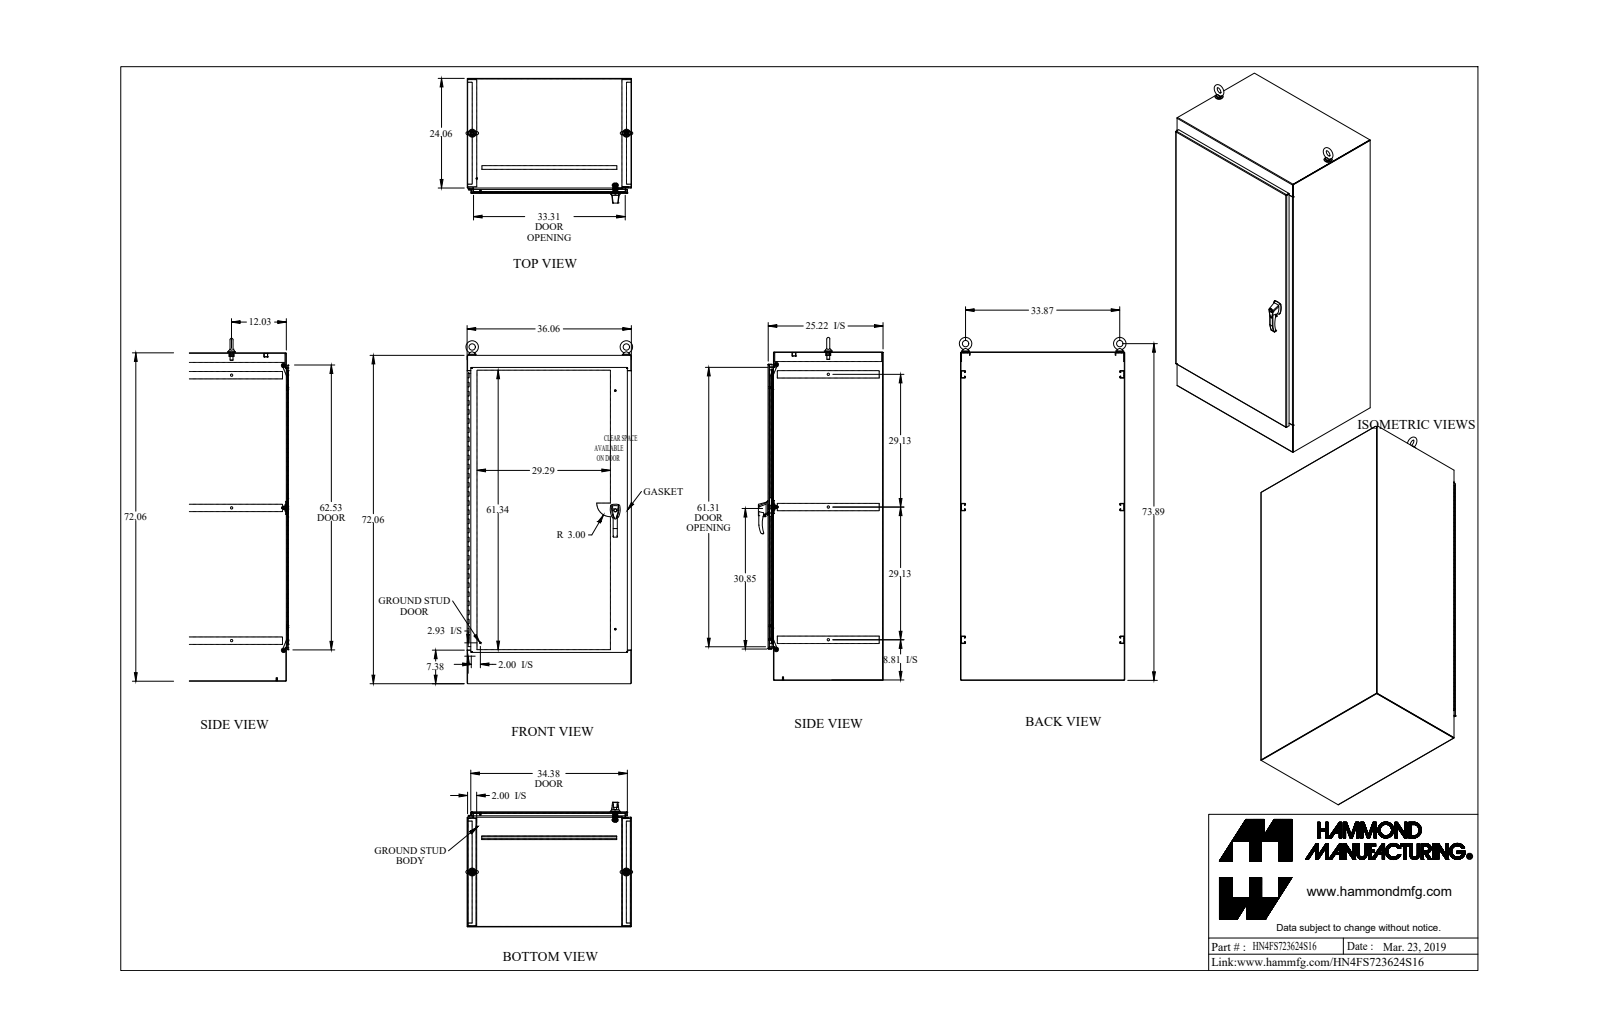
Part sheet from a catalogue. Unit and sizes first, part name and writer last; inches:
Units: inches
Overall size (bounding box): 75.489 × 36.604 × 27.362
Round holes (diameter × count): ⌀0.304 ×10, ⌀0.35 ×7, ⌀0.5 ×3, ⌀0.25 ×2, ⌀0.257 ×2, ⌀0.28 ×2, ⌀0.281 ×2, ⌀0.313 ×2, ⌀0.39 ×2, ⌀0.413 ×2, ⌀0.527 ×2, ⌀0.68 ×2
Round bosses / shafts (diameter × count): ⌀1.75 ×2, ⌀1.5 ×2, ⌀1.25 ×2, ⌀1 ×2, ⌀0.75 ×2, ⌀0.738 ×2, ⌀0.63 ×2, ⌀0.625 ×2
Partial cylindrical surfaces — rounded edges, fillets, slot ends (radius × count): R0.043 ×42, R0.138 ×36, R0.5 ×23, R0.125 ×22, R0.018 ×16, R0.06 ×15, R0.048 ×13, R0.143 ×13
Main face-to-face distances: 0.095, 25.152, 35.965, 25.057, 25.247, 35.87, 36.06, 71.965, 23.965, 1.187
Hole centre spacings: 6, 12, 18, 24, 30, 36, 42, 0.015
Volume: 1 180 in³ · Surface area: 24 827 in²
Bodies: 57 solids, 1892 faces (877 planar, 850 cylindrical, 165 other)
Part name (STEP PRODUCT): HN4FS723624S16
STEP written by: SolidWorks 2018 (AUTOMOTIVE_DESIGN)
